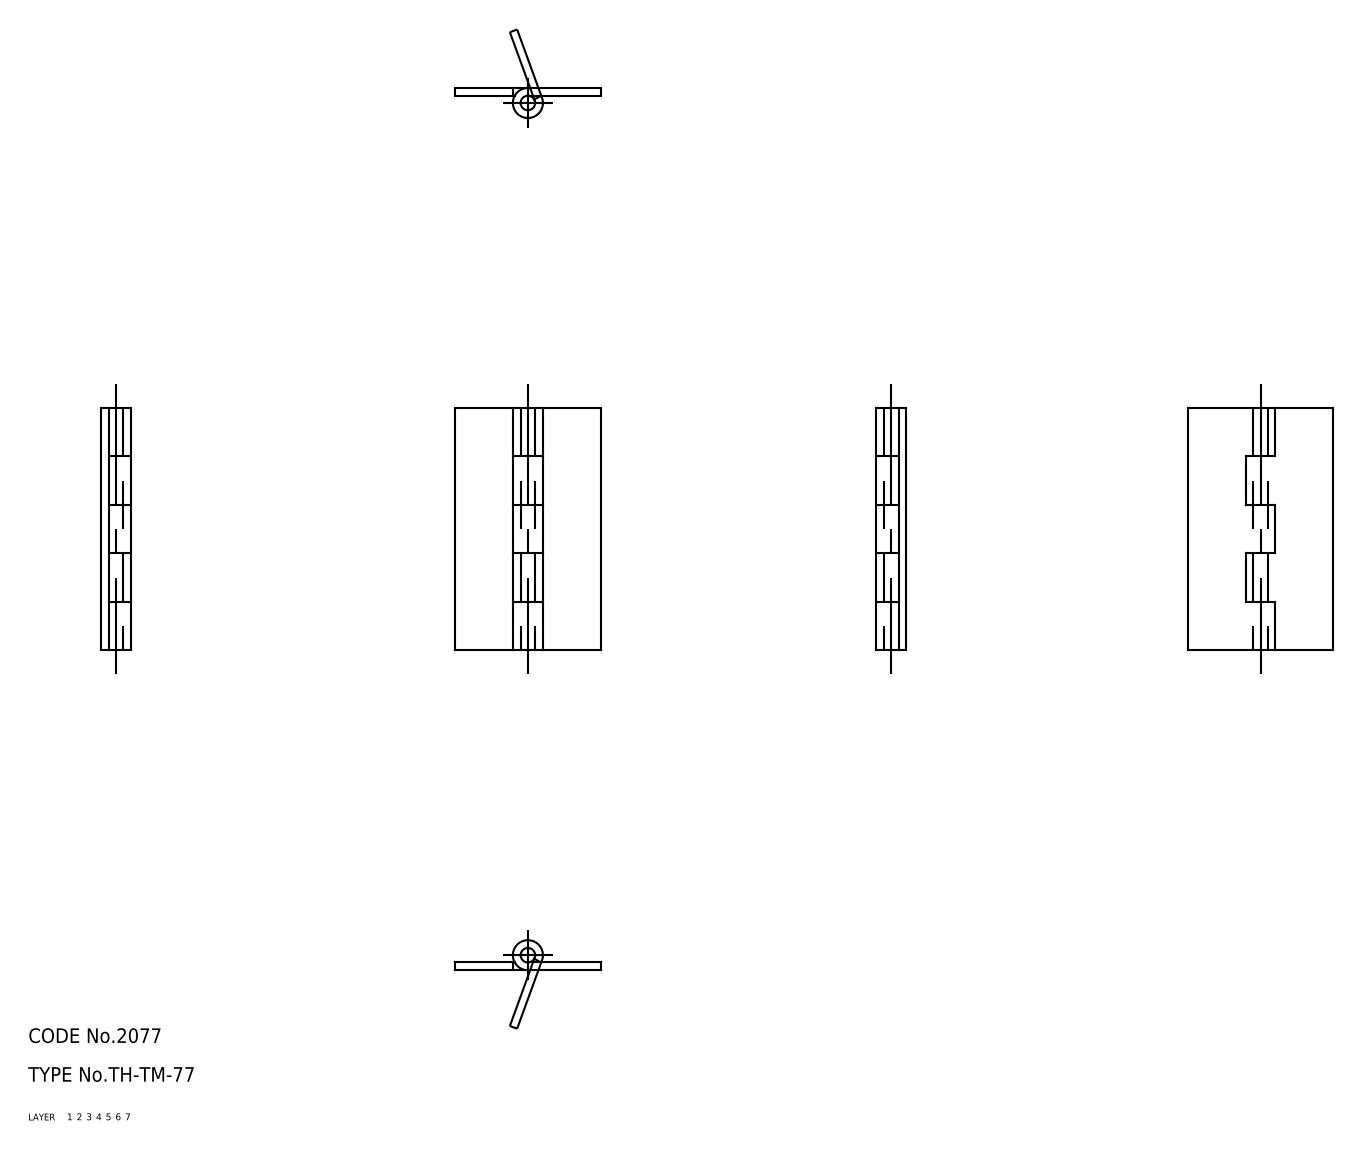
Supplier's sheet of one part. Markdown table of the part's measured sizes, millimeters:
| quantity | value |
| --- | --- |
| part name | hinge piece_B; hinge piece_A; shaft; TH_TM_77_25517_36 |
| STEP written by | CADfix (AUTOMOTIVE_DESIGN) |
| units | millimeters |
| bodies | 3 solids, 42 faces (0 planar, 0 cylindrical, 42 other) |
| overall size | 50 × 30 × 6.2 |
| volume | 3 463 mm³ |
| surface area | 5 009 mm² |
